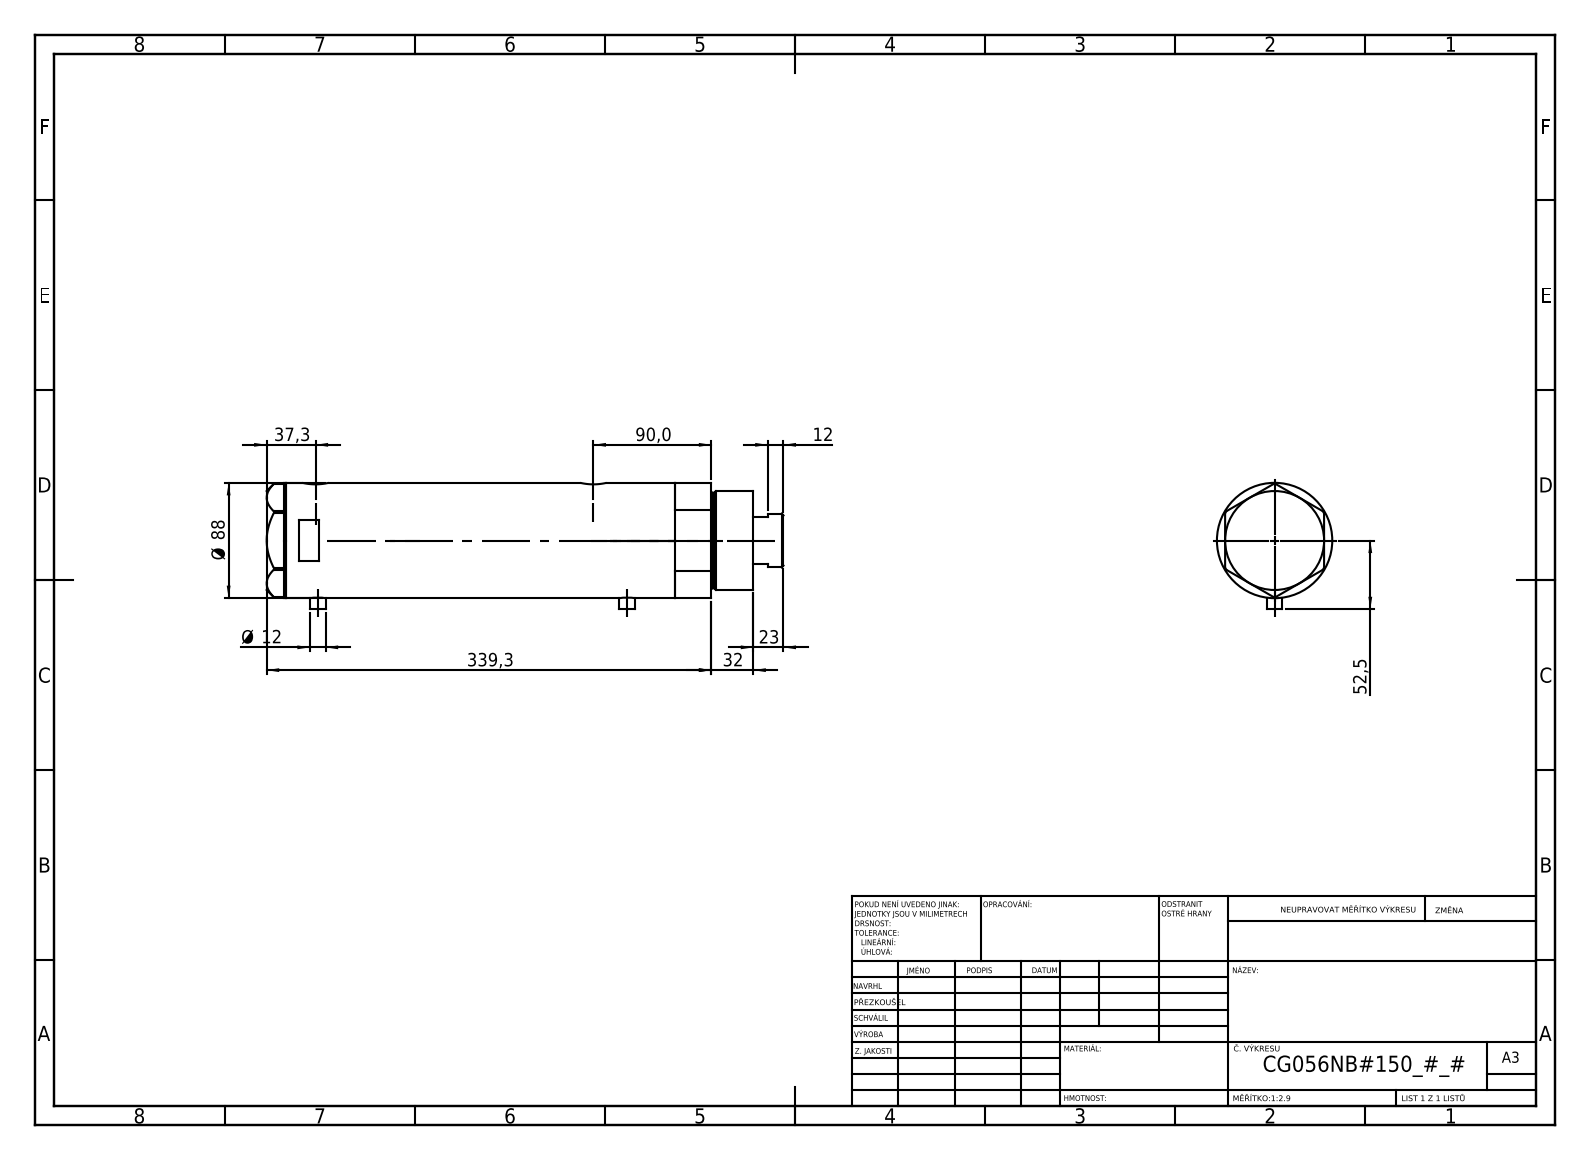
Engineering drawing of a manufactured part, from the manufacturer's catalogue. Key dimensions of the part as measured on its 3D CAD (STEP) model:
Part name (STEP PRODUCT): V270CG_MIDDLE; V270CG_FRONT; V270CG_VC; V270CG_BACK
STEP written by: SolidWorks 2019 (CONFIG_CONTROL_DESIGN)
Units: millimetres
Bodies: 4 solids, 121 faces (52 planar, 49 cylindrical, 20 other)
Overall size (bounding box): 394.3 × 96.5 × 88
Volume: 2 034 000 mm³ · Surface area: 279 868 mm²
Round holes (diameter × count): ⌀12.5 ×2, ⌀13.16 ×2, ⌀20 ×2, ⌀14.5 ×1, ⌀42 ×1, ⌀43.5 ×1, ⌀56 ×1, ⌀60 ×1, ⌀80 ×1
Round bosses / shafts (diameter × count): ⌀12 ×2, ⌀88 ×1, ⌀75 ×1, ⌀73 ×1, ⌀41 ×1
Main face-to-face distances: 234.4, 26, 208.4, 15, 41, 249.4, 356.3, 371.3, 330.3, 121.9
Hole centre spacings: 1.7, 25.8, 210.3, 212, 236.1, 237.8
